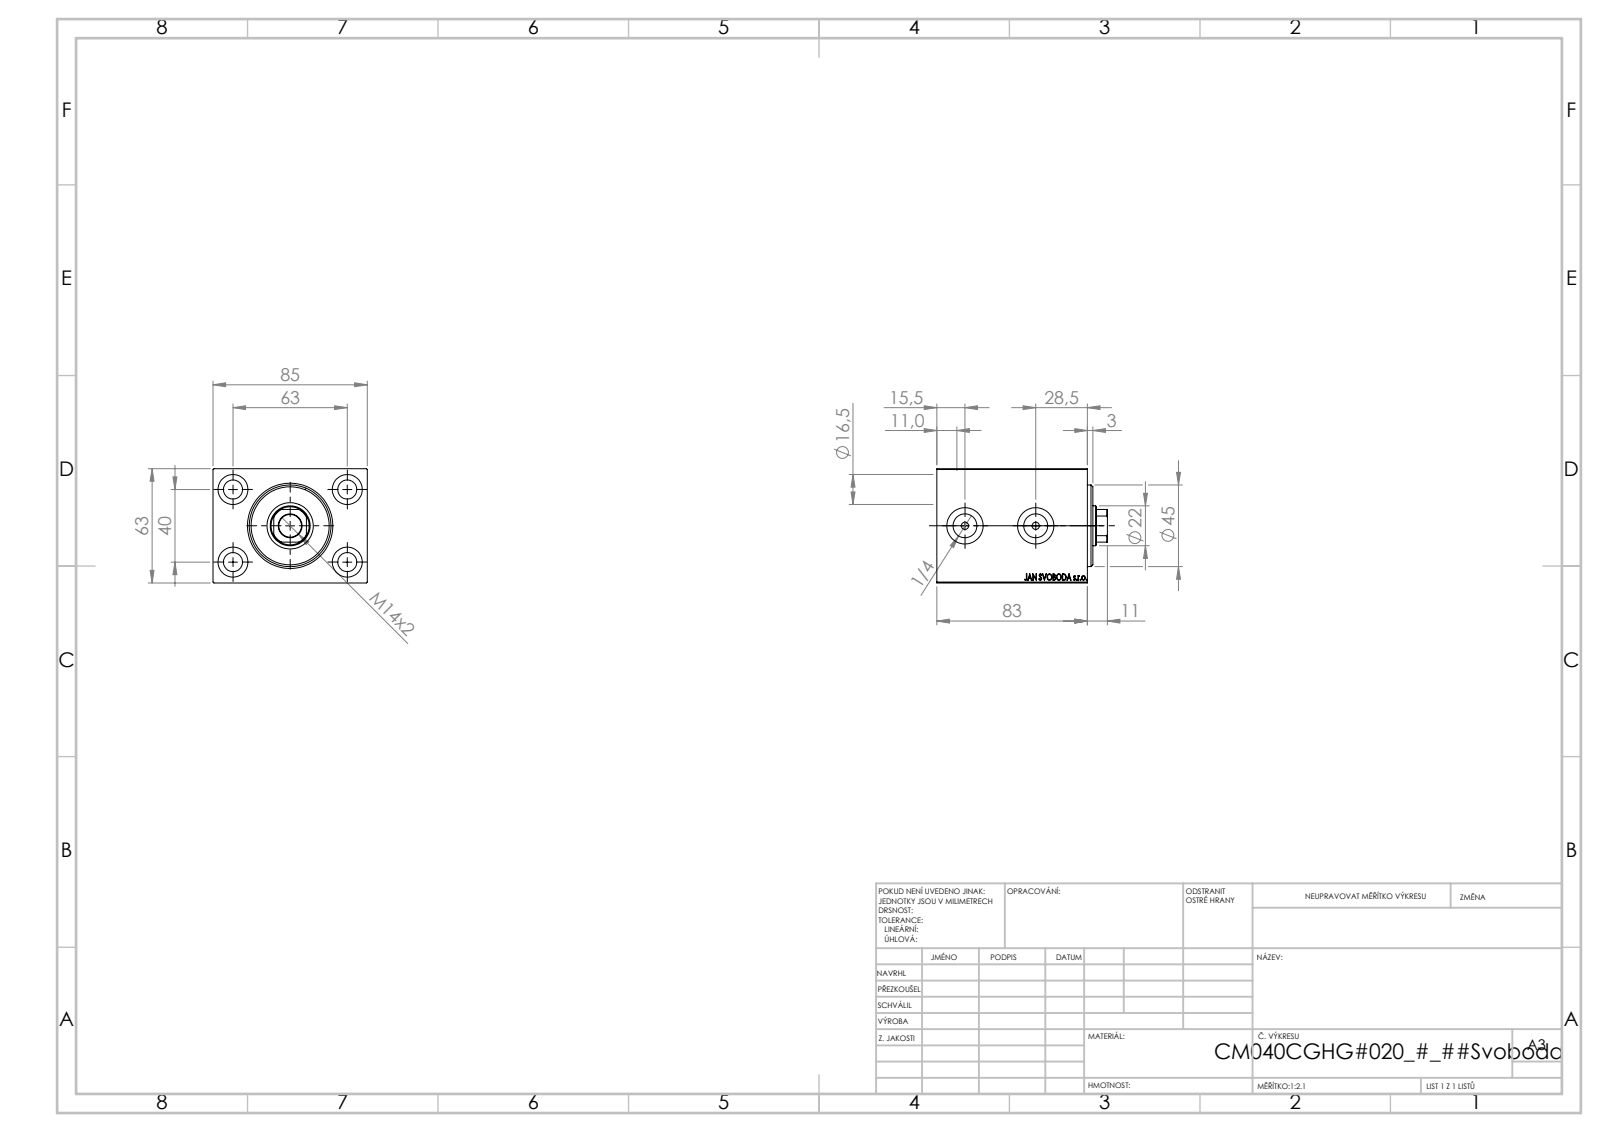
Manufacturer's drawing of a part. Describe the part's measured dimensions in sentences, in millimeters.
The part is named "V450CM_C_Body; V450CM_VC_B; V450CM_C_VCP". Its 3-D file was written by "SolidWorks 2019 (CONFIG_CONTROL_DESIGN)". It is 3 solids with 863 faces: 409 planar, 60 cylindrical and 394 other. Overall it measures 94 by 85 by 63 millimeters. Its volume is 396 142 cubic millimeters and its surface area 71 277 square millimeters. Round holes: 4 of diameter 10.5, 4 of diameter 16.5, 2 of diameter 4, 2 of diameter 13.16, 2 of diameter 20, 1 of diameter 12.5, 1 of diameter 22, 1 of diameter 25.5, 1 of diameter 40, 1 of diameter 42, 1 of diameter 45. Partial cylindrical surfaces (rounded edges, fillets, slot ends): 1 of radius 10.5. The main face-to-face distances are 63, 85, 83, 32, 51, 72, 11, 21.6, 29.4, 61.4. The hole center spacings are 37.31, 40, 63, 74.63, 39.
